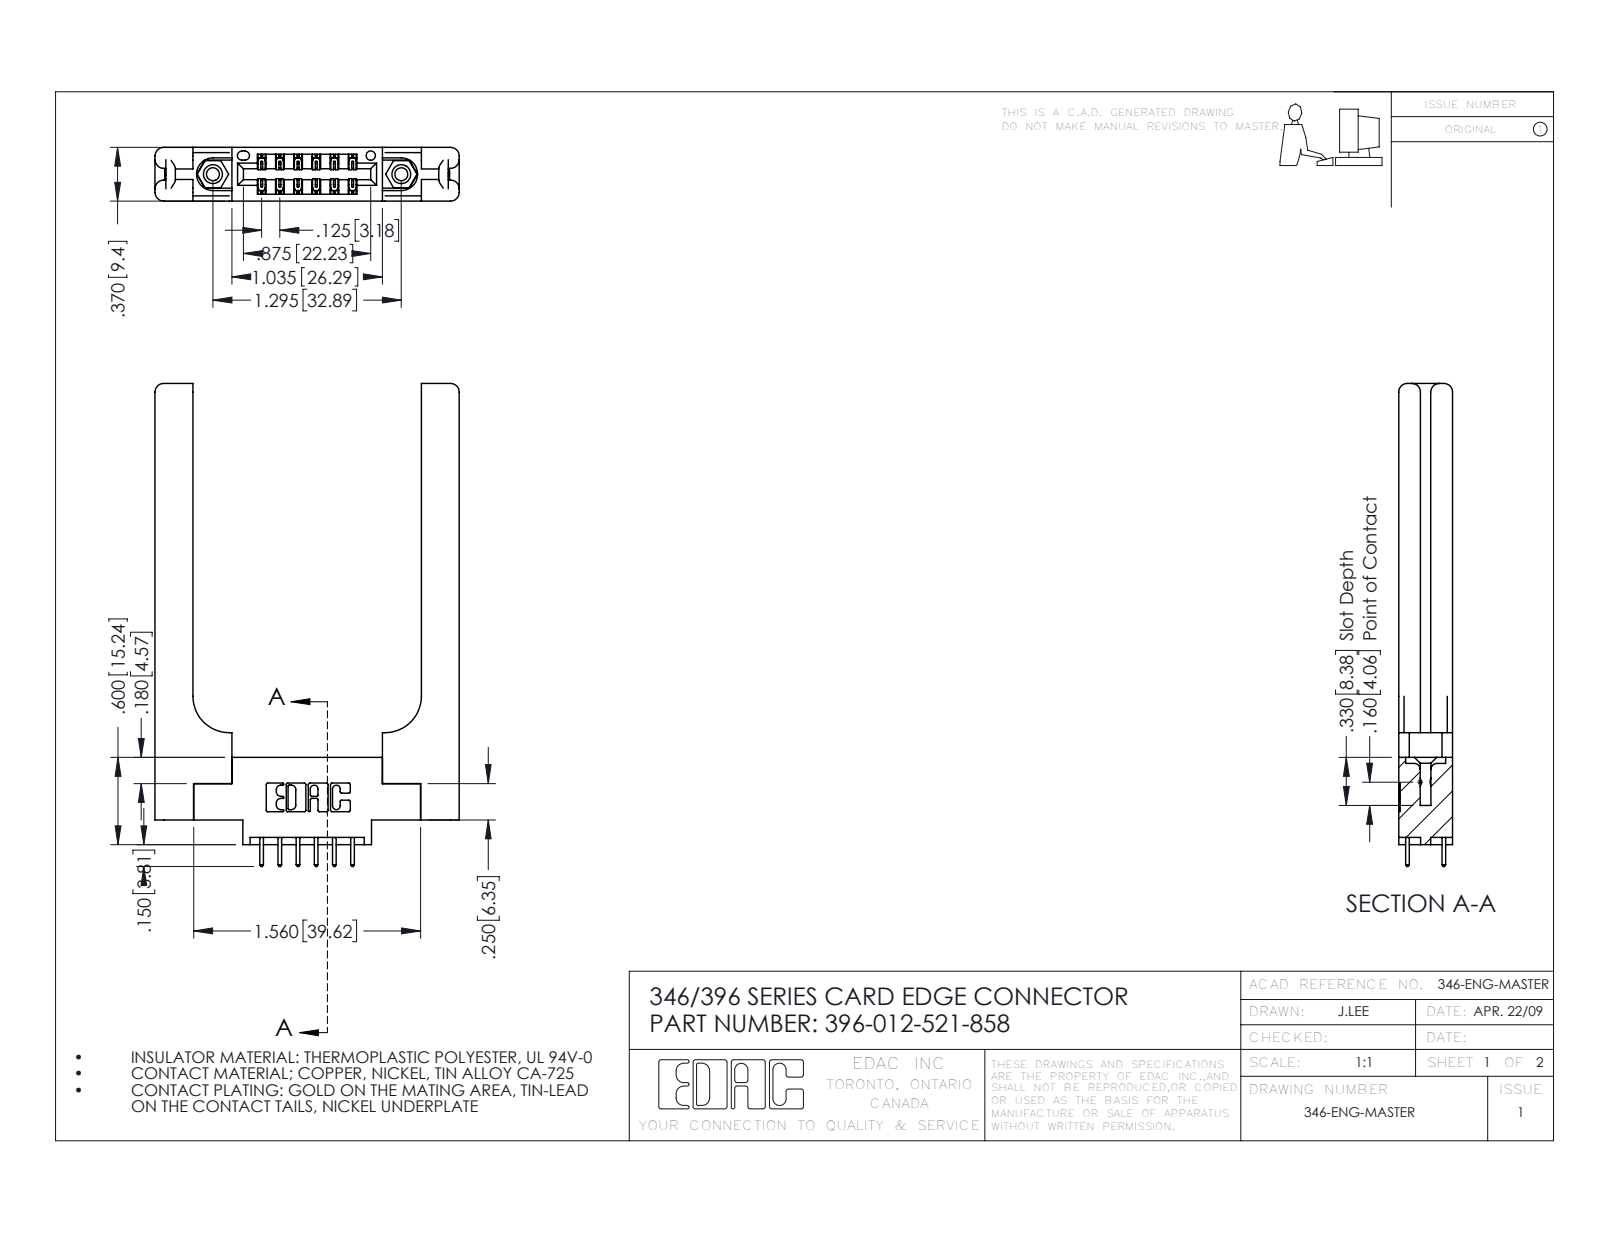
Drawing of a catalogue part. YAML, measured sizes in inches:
part_name: "346 Part_0.170 Offset - 0.156 Dia-TH; 345-250-001_345-250-001-102; 345-292-001_345-293-121; 346-220-058_345-220-058 (+1 more)"
step_written_by: "SolidWorks 2016 (CONFIG_CONTROL_DESIGN)"
units: inches
bodies: {solids: 17, faces: 1006, planar: 648, cylindrical: 298, other: 60}
overall_size: [3.32, 2.091, 0.37]
volume: 0.747
surface_area: 17.16
round_holes:
  - {diameter: 0.089, count: 2}
  - {diameter: 0.125, count: 2}
  - {diameter: 0.156, count: 2}
  - {diameter: 0.064, count: 1}
round_bosses_or_shafts:
  - {diameter: 0.155, count: 2}
partial_cylinders:
  - {radius: 0.01, count: 22}
  - {radius: 0.006, count: 18}
  - {radius: 0.06, count: 16}
  - {radius: 0.01, count: 12}
  - {radius: 0.007, count: 6}
  - {radius: 0.031, count: 6}
  - {radius: 0.026, count: 3}
  - {radius: 0.014, count: 2}
face_to_face_distances: [0.37, 0.15, 0.22, 0.072, 0.25, 0.148, 1.571, 0.102, 0.048, 0.322]
hole_center_spacings: [0.246, 1.092, 1.295]
